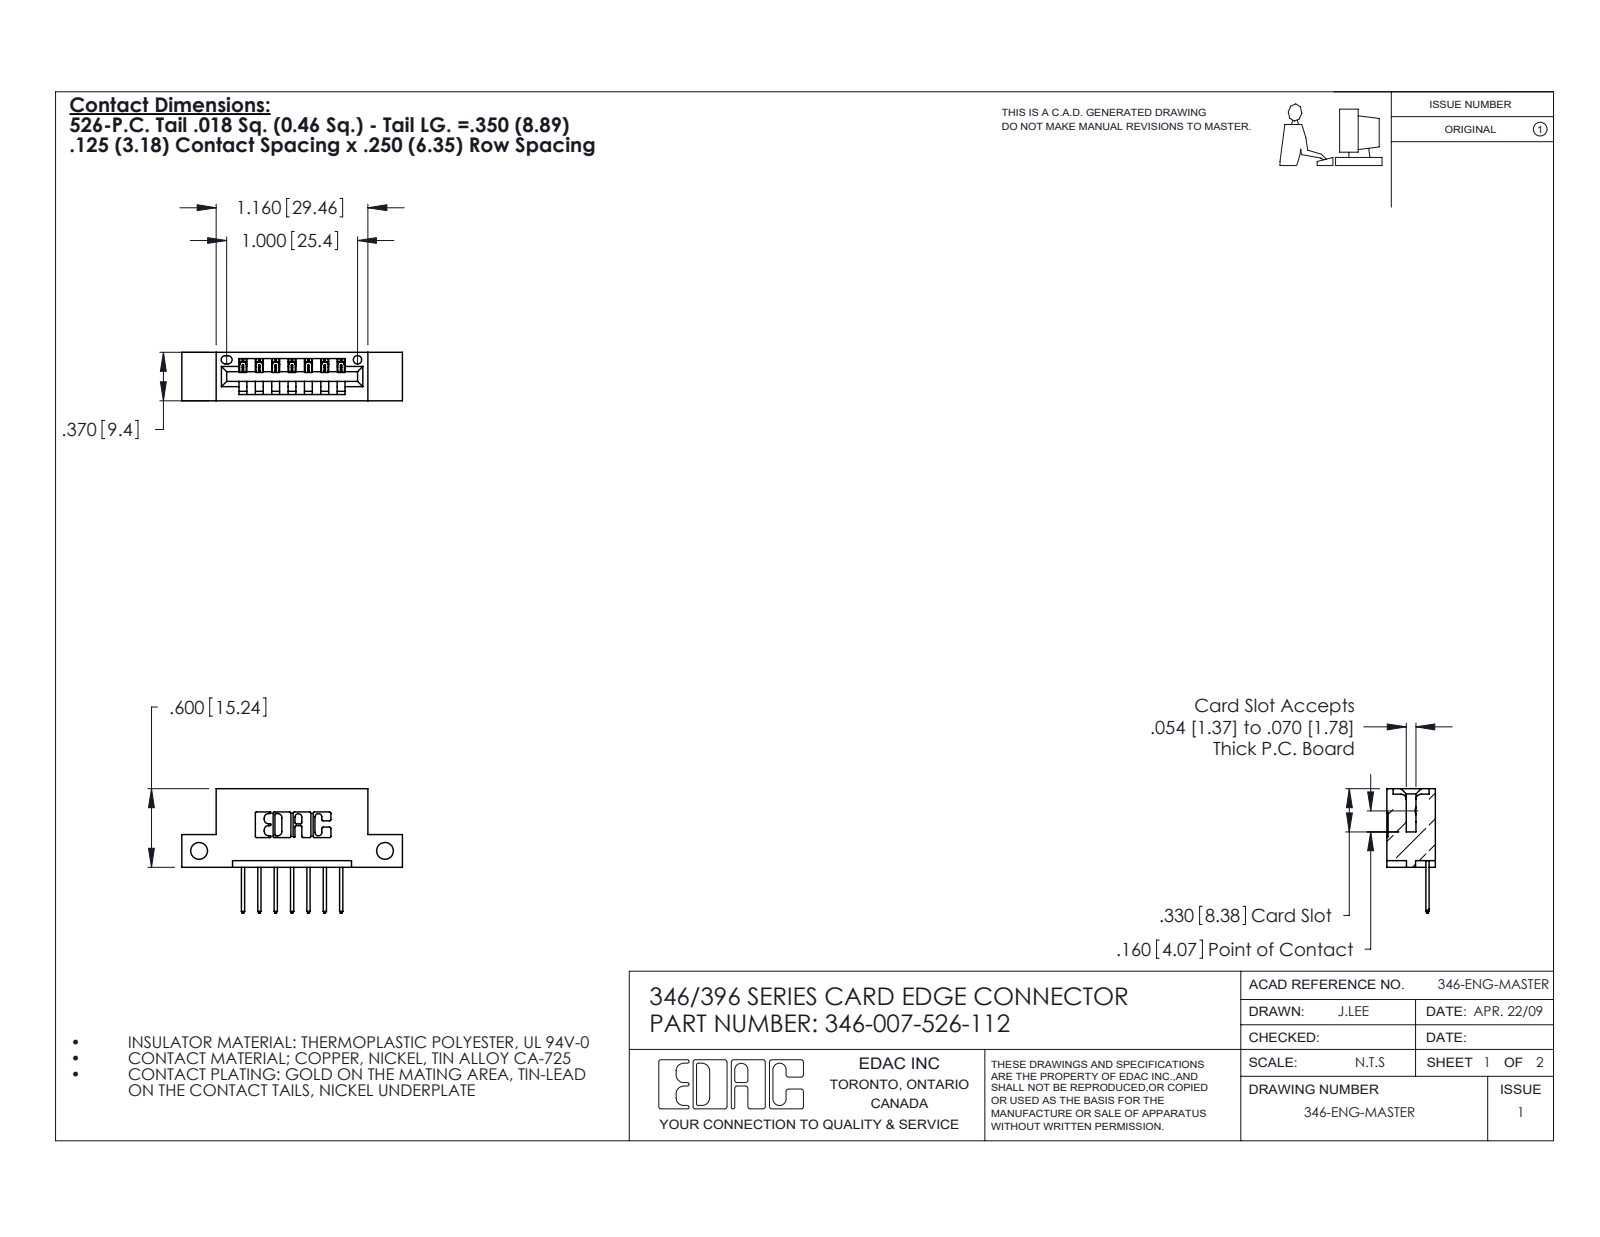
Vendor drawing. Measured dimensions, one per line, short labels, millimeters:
name: 345-292-001_345-293-126; 346-007-526-112; 346 Part_Flush Mounting Lugs - Side Mount
written by: SolidWorks 2020 (CONFIG_CONTROL_DESIGN)
unit: mm
bodies: 8 solids, 528 faces (356 planar, 172 cylindrical, 0 other)
size: 42.8 × 24.1 × 9.4
volume: 3 770 mm³; area: 4 173 mm²
holes: 2× ⌀3.3, 1× ⌀1.6
rounds: 22× R0.3, 14× R0.2, 14× R0.3, 6× R0.2, 6× R0.8, 3× R0.7, 2× R0.8, 2× R1
face distances: 6.4, 9.4, 1.2, 8.2, 3.8, 5.6, 2.5, 4.4, 1.8, 7.6
hole spacings: 36.1
